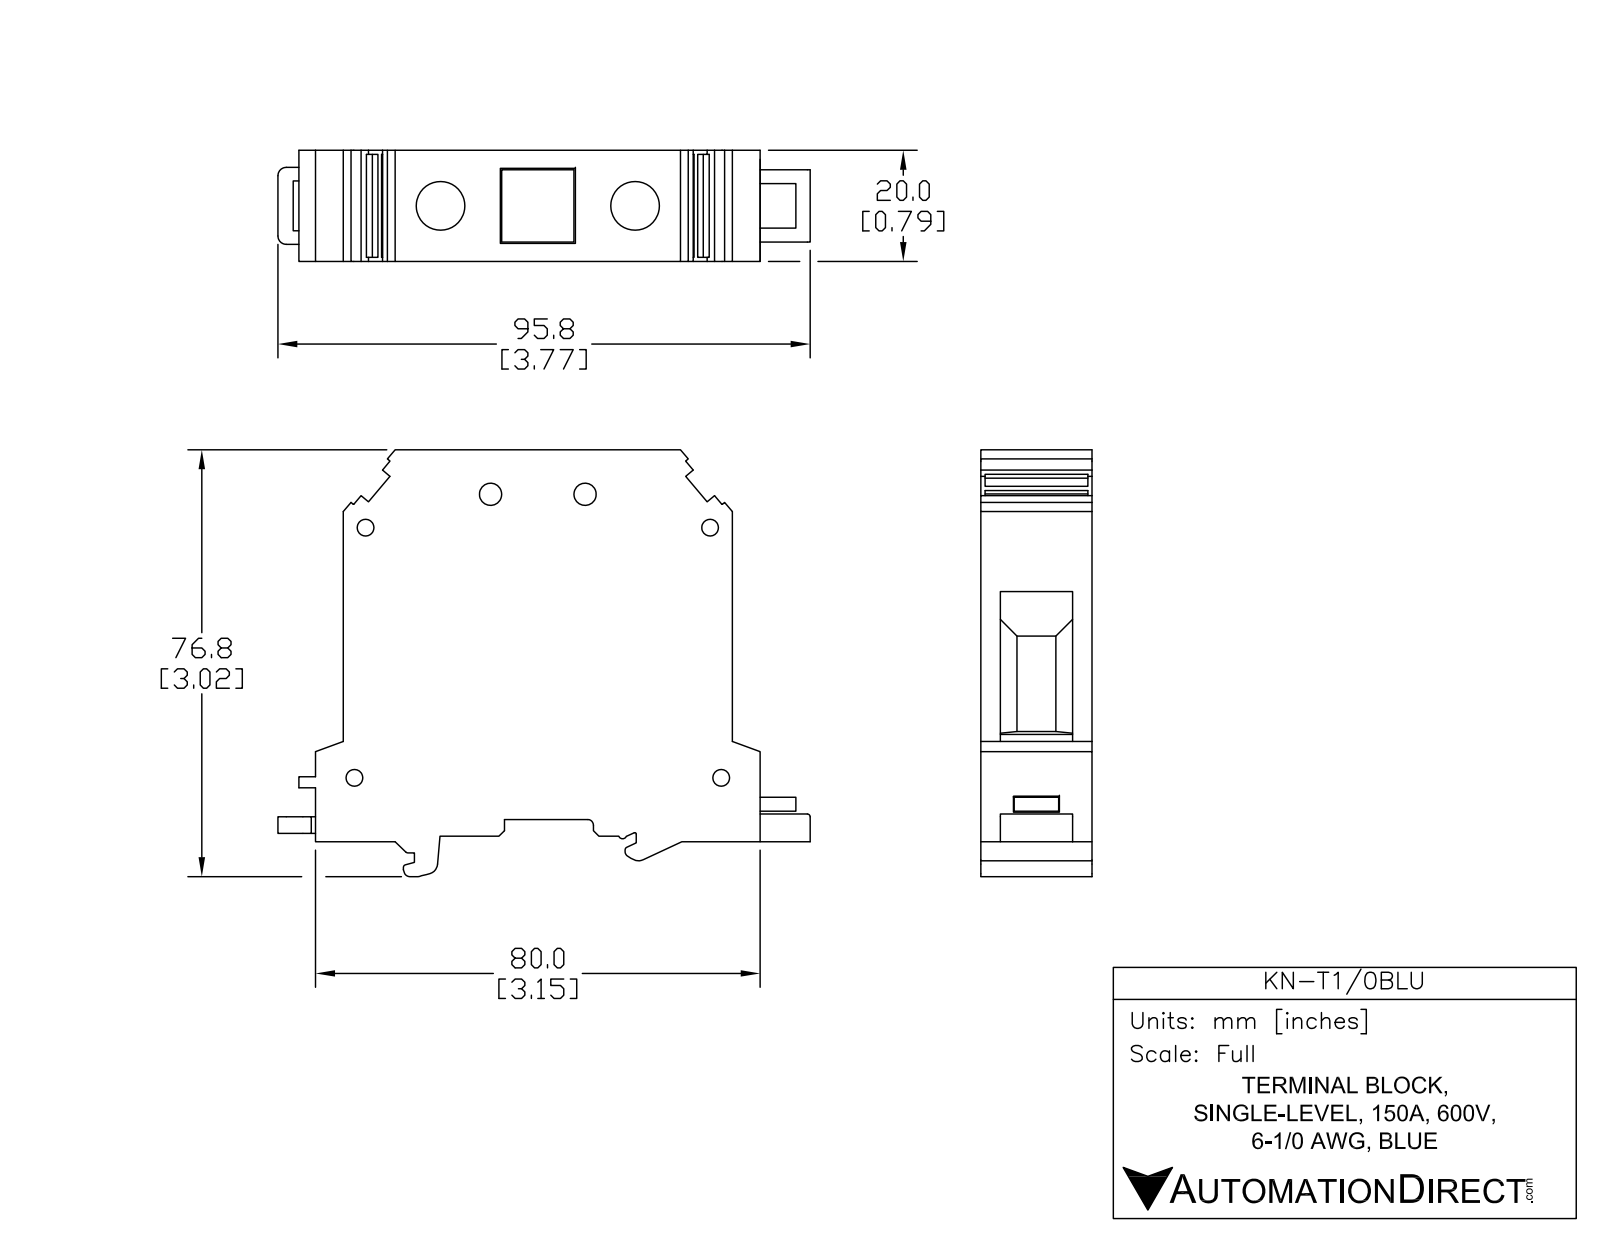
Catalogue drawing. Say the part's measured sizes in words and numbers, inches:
The part is named "KN-T1_0BLU". Its 3-D file was written by "SolidWorks 2019 (CONFIG_CONTROL_DESIGN)". It is 1 solid with 346 faces: 257 planar, 68 cylindrical and 21 other. Overall it measures 3.77 by 3.027 by 0.945 inches. Its volume is 5.975 cubic inches and its surface area 29.34 square inches. Round holes: 2 of diameter 0.335, 1 of diameter 0.079. Round bosses or shafts: 2 of diameter 0.157. Partial cylindrical surfaces (rounded edges, fillets, slot ends): 9 of radius 0.039, 6 of radius 0.02, 5 of radius 0.004, 5 of radius 0.012, 3 of radius 0.03, 3 of radius 0.079, 2 of radius 0.049, 2 of radius 0.059. The main face-to-face distances are 0.787, 0.039, 2.717, 2.776, 0.197, 0.236, 2.913, 2.953, 2.677, 0.138. The hole center spacings are 1.378.
